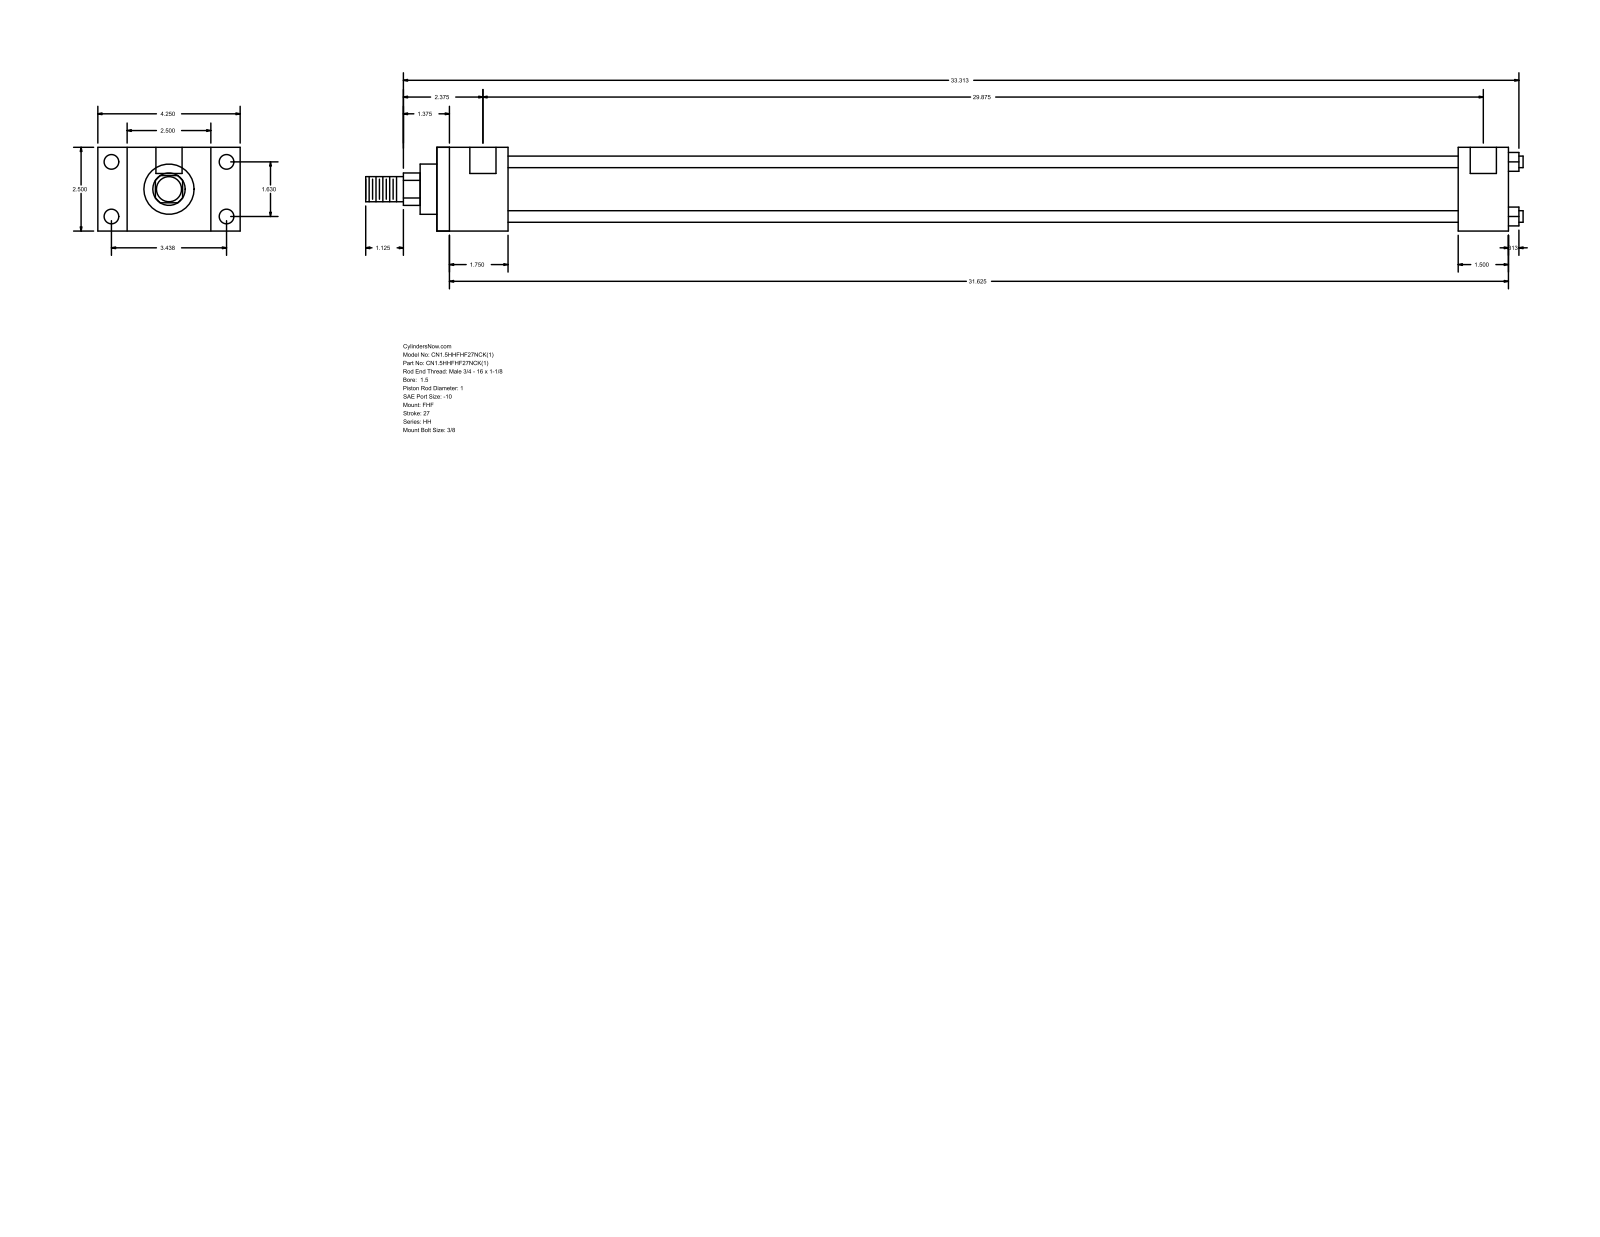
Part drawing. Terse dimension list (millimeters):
name: HH_FHF__0150_1
written by: GSSL Pune (CONFIG_CONTROL_DESIGN)
unit: mm
bodies: 0 solids, 88 faces (60 planar, 28 cylindrical, 0 other)
size: 877.89 × 107.95 × 63.5
holes: 4× ⌀5.56, 4× ⌀11.13, 2× ⌀19.84
bosses: 4× ⌀8.76, 1× ⌀44.45, 1× ⌀38.1, 1× ⌀25.4, 1× ⌀19.05
rounds: 1× R12.29
face distances: 63.5, 22.23, 85.73, 53.98, 107.96, 812.8, 758.82, 38.1, 774.7, 720.72
hole spacings: 1.59, 41.4, 87.32, 96.64, 760.41, 762, 758.82
